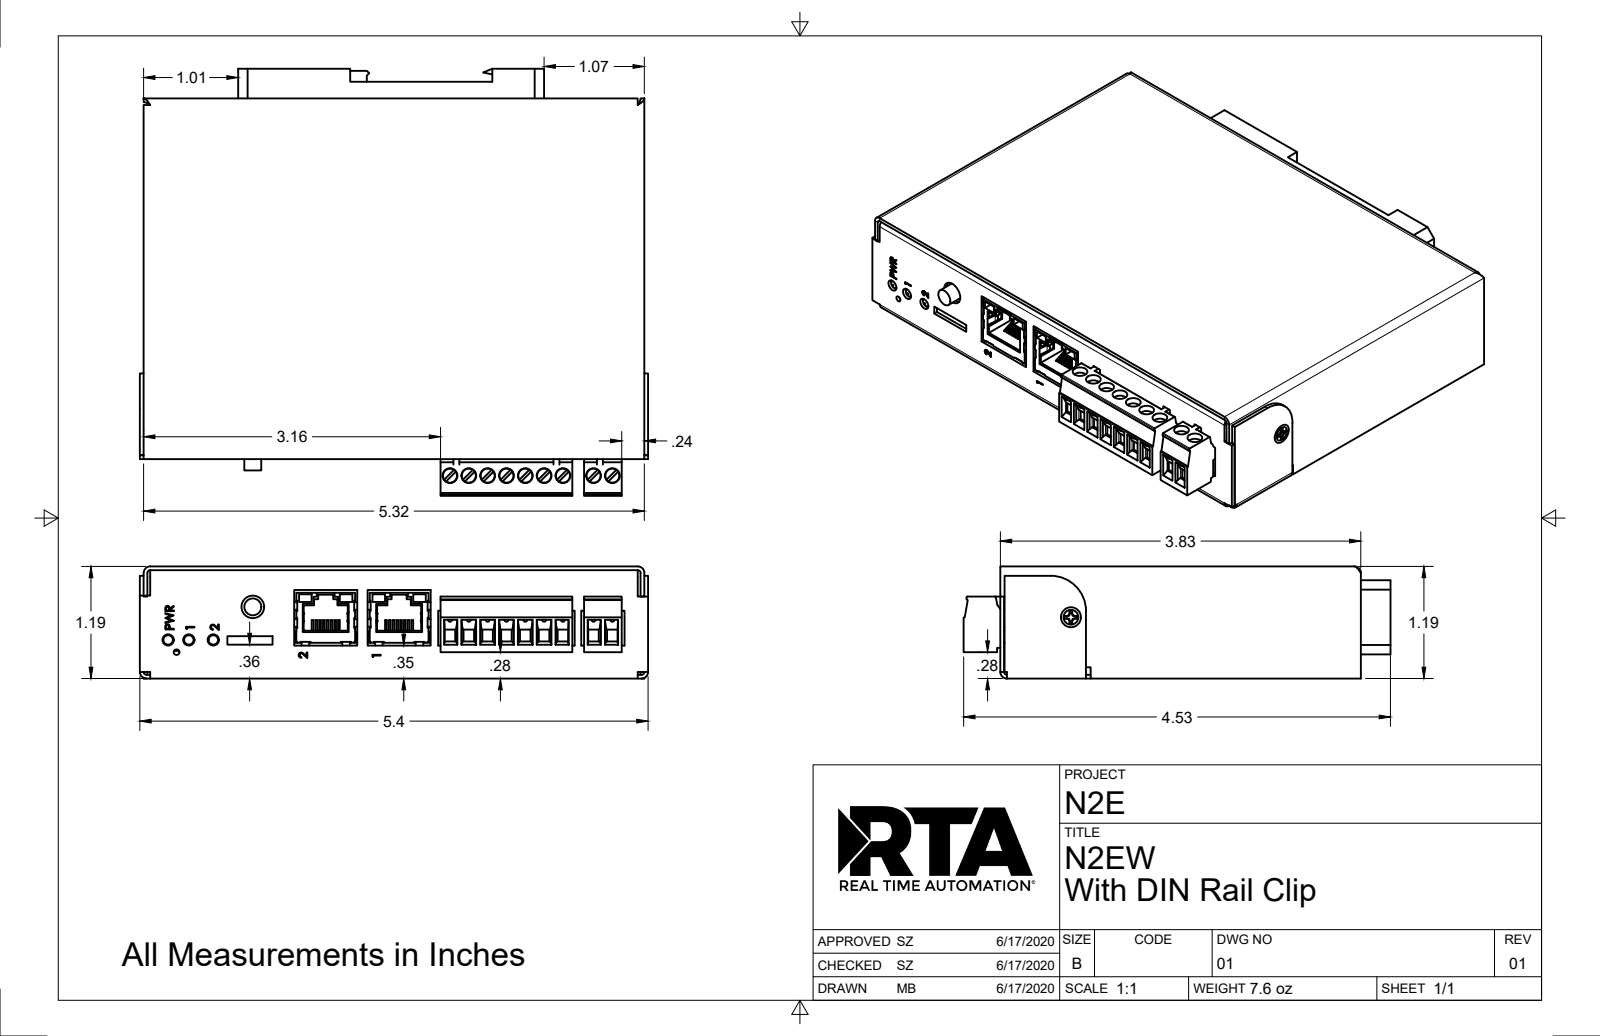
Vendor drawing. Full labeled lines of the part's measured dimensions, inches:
Part name (STEP PRODUCT): N2E v2
STEP written by: Autodesk Translation Framework v9.3.0.1241 (AUTOMOTIVE_DESIGN)
Units: inches
Bodies: 15 solids, 1449 faces (1091 planar, 288 cylindrical, 70 other)
Overall size (bounding box): 5.4 × 4.535 × 1.19
Volume: 4.277 in³ · Surface area: 162.2 in²
Round holes (diameter × count): ⌀0.055 ×9, ⌀0.157 ×9, ⌀0.11 ×7, ⌀0.125 ×4, ⌀0.12 ×3, ⌀0.129 ×2, ⌀0.13 ×2, ⌀0.34 ×2, ⌀0.06 ×1, ⌀0.089 ×1, ⌀0.157 ×1, ⌀0.24 ×1
Round bosses / shafts (diameter × count): ⌀0.149 ×9, ⌀0.165 ×4, ⌀0.112 ×3, ⌀0.078 ×3, ⌀0.25 ×2, ⌀0.18 ×1, ⌀0.14 ×1, ⌀0.024 ×1
Partial cylindrical surfaces — rounded edges, fillets, slot ends (radius × count): R0.03 ×12, R0.008 ×10, R0.02 ×9, R0.115 ×9, R0.02 ×8, R0.07 ×8, R0.01 ×4, R0.011 ×4
Main face-to-face distances: 0.04, 1.15, 1.19, 1.11, 0.043, 5.28, 0.04, 5.32, 0.083, 3.747
Hole centre spacings: 0.2, 0.4, 0.6, 0.8, 0.525, 0.725, 0.925, 1
